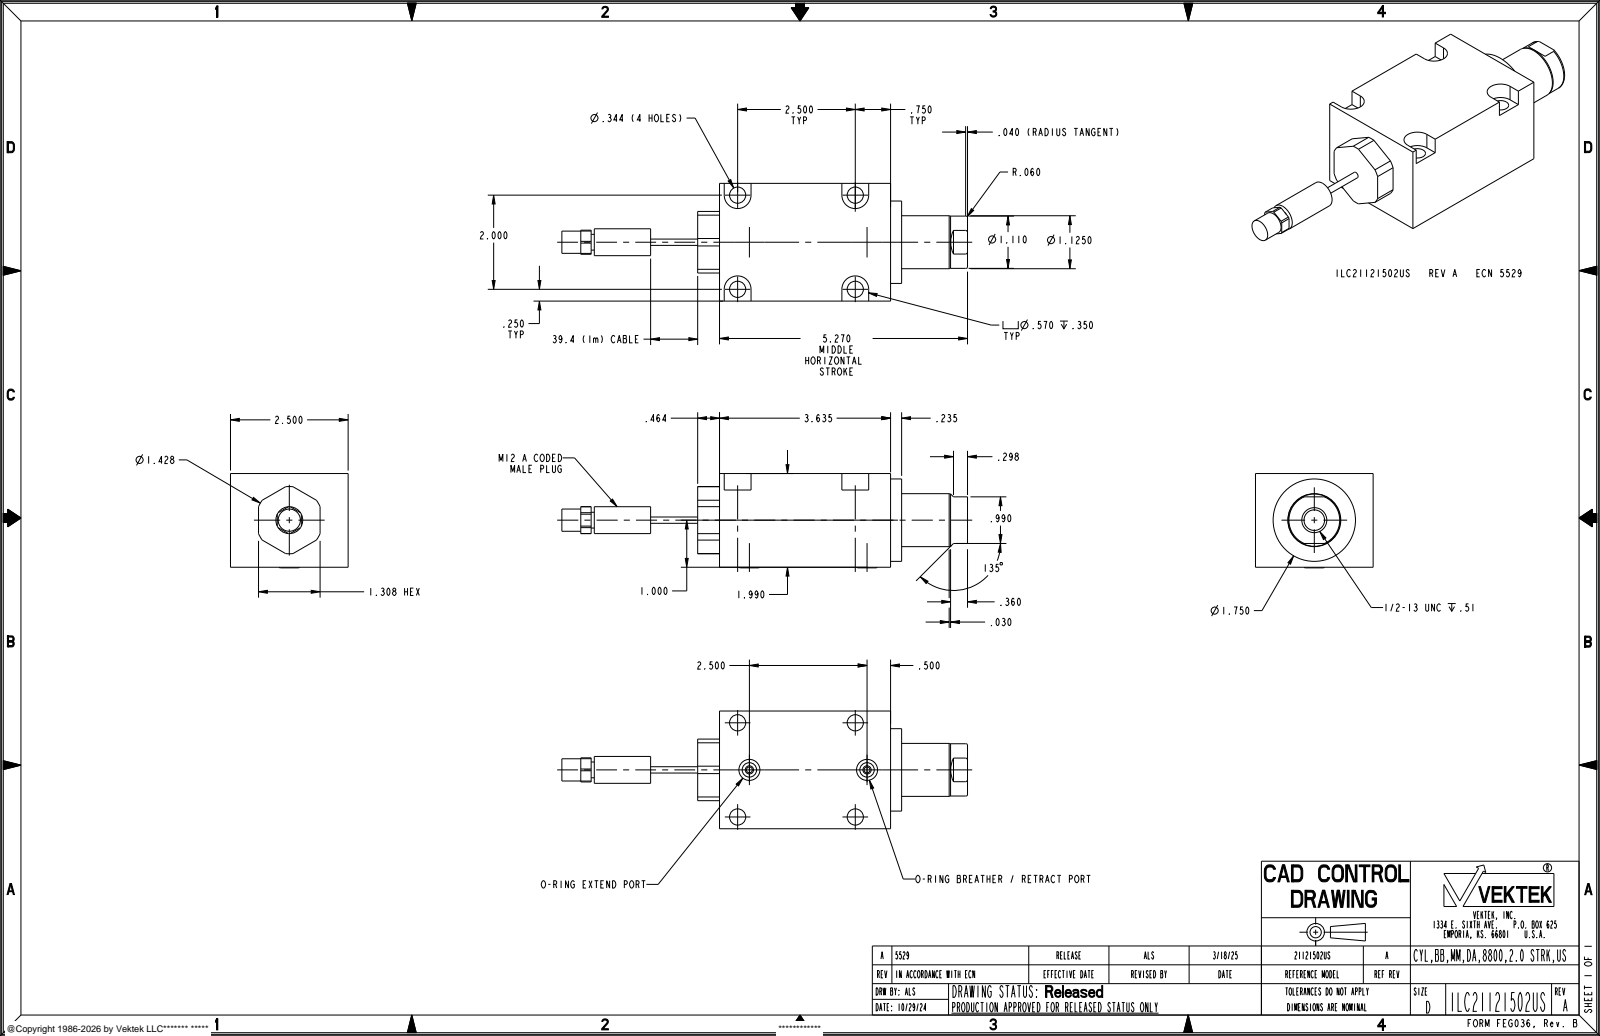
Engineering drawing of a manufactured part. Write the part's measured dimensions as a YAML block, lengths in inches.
part_name: "ILC21121502US"
step_written_by: "CREO PARAMETRIC BY PTC INC, 2021164 (AUTOMOTIVE_DESIGN)"
units: inches
bodies: {solids: 1, faces: 120, planar: 46, cylindrical: 52, other: 22}
overall_size: [8.62, 2.7, 2.003]
volume: 20.04
surface_area: 65.21
round_holes:
  - {diameter: 0.344, count: 4}
  - {diameter: 0.125, count: 2}
  - {diameter: 0.447, count: 2}
  - {diameter: 0.437, count: 1}
round_bosses_or_shafts:
  - {diameter: 1.75, count: 1}
  - {diameter: 1.125, count: 1}
  - {diameter: 1.11, count: 1}
  - {diameter: 0.571, count: 1}
  - {diameter: 0.5, count: 1}
  - {diameter: 0.472, count: 1}
  - {diameter: 0.335, count: 1}
  - {diameter: 0.134, count: 1}
partial_cylinders:
  - {radius: 0.285, count: 4}
  - {radius: 0.714, count: 1}
face_to_face_distances: [1.99, 2.5, 3.635, 4.099, 0.464, 0.235, 3.87, 4.334, 1.308, 1.64]
hole_center_spacings: [1.031, 2.5, 2, 2.462, 2.926, 3.202]
